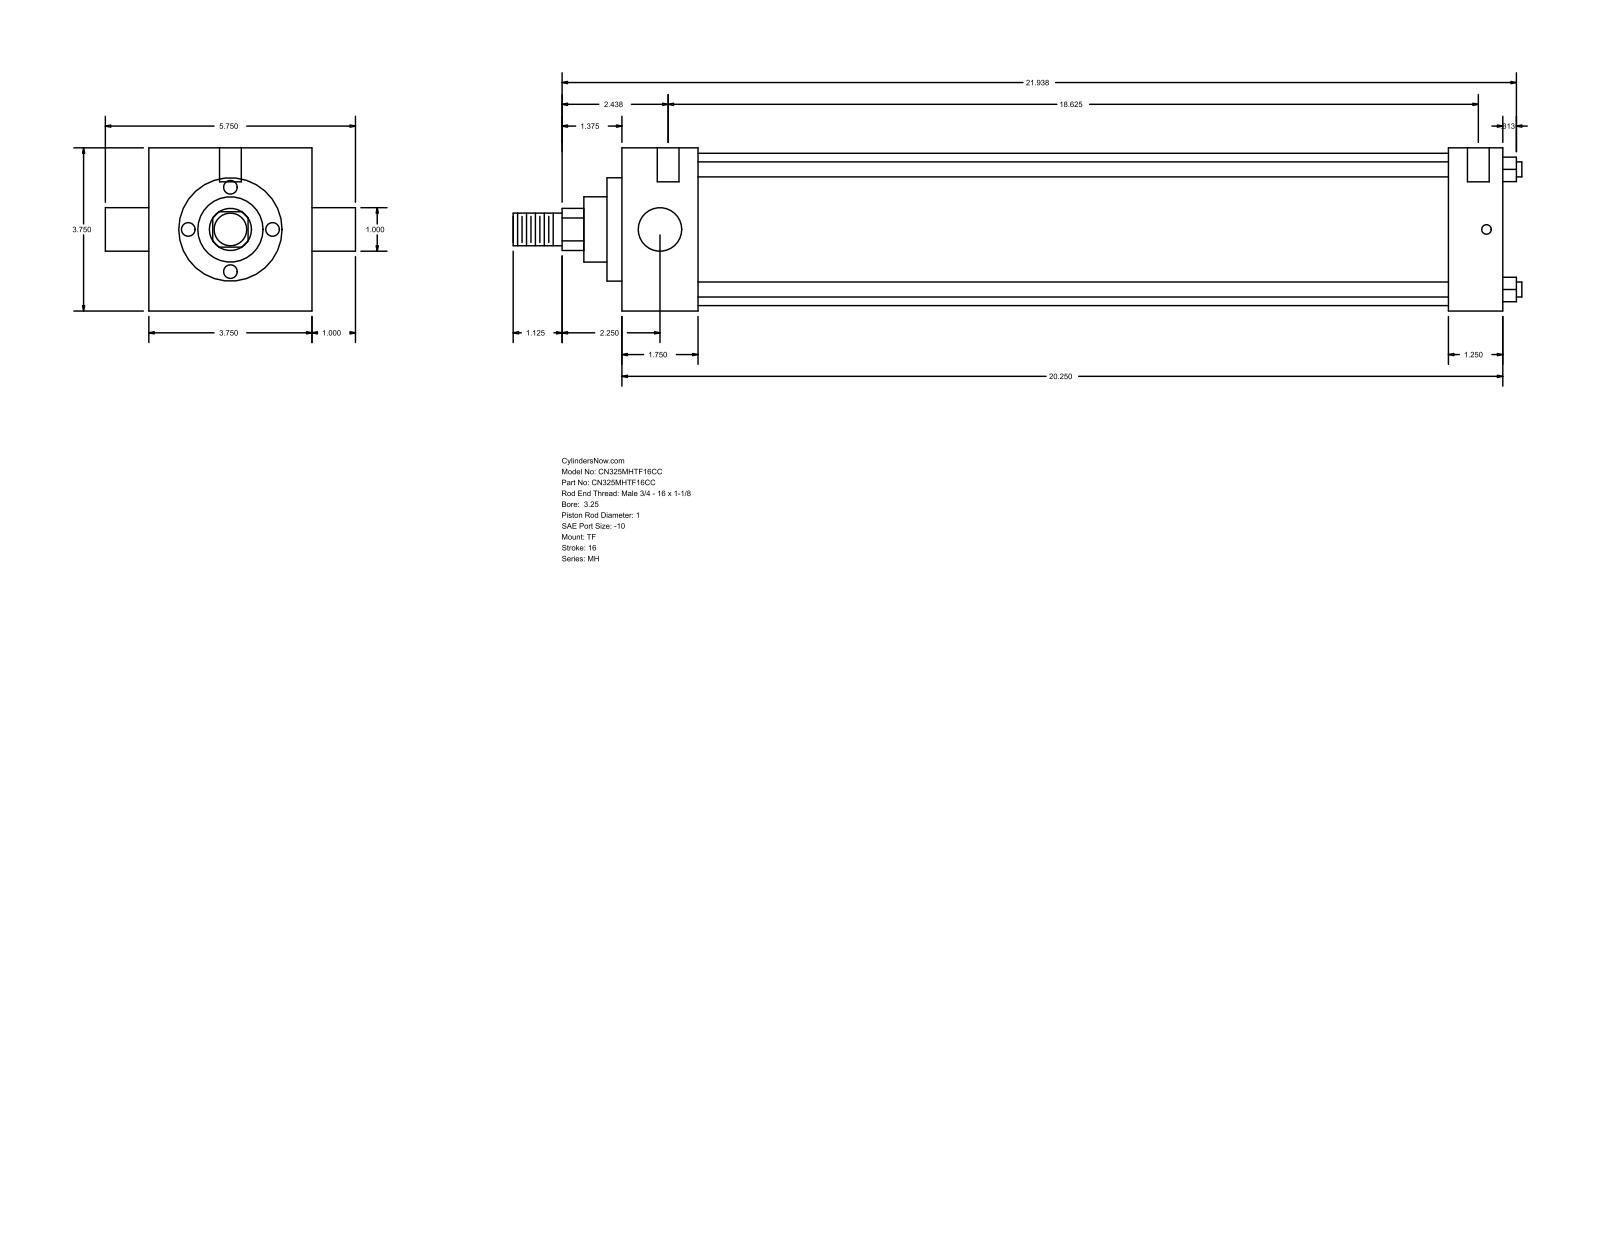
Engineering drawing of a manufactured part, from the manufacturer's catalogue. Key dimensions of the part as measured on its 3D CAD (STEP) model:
Part name (STEP PRODUCT): MH_TF__0325_1
STEP written by: GSSL Pune (CONFIG_CONTROL_DESIGN)
Units: millimetres
Bodies: 0 solids, 86 faces (61 planar, 25 cylindrical, 0 other)
Overall size (bounding box): 588.96 × 146.05 × 95.25
Round holes (diameter × count): ⌀5.56 ×3, ⌀12.7 ×2
Round bosses / shafts (diameter × count): ⌀8.76 ×4, ⌀25.4 ×2, ⌀88.9 ×1, ⌀60.33 ×1, ⌀38.1 ×1, ⌀19.05 ×1
Partial cylindrical surfaces — rounded edges, fillets, slot ends (radius × count): R12.29 ×1
Main face-to-face distances: 95.24, 514.35, 44.46, 482.6, 438.14, 469.89, 31.75, 8.73, 53.19, 491.33
Hole centre spacings: 1.58, 4.76, 473.08, 474.66, 477.84, 479.42
